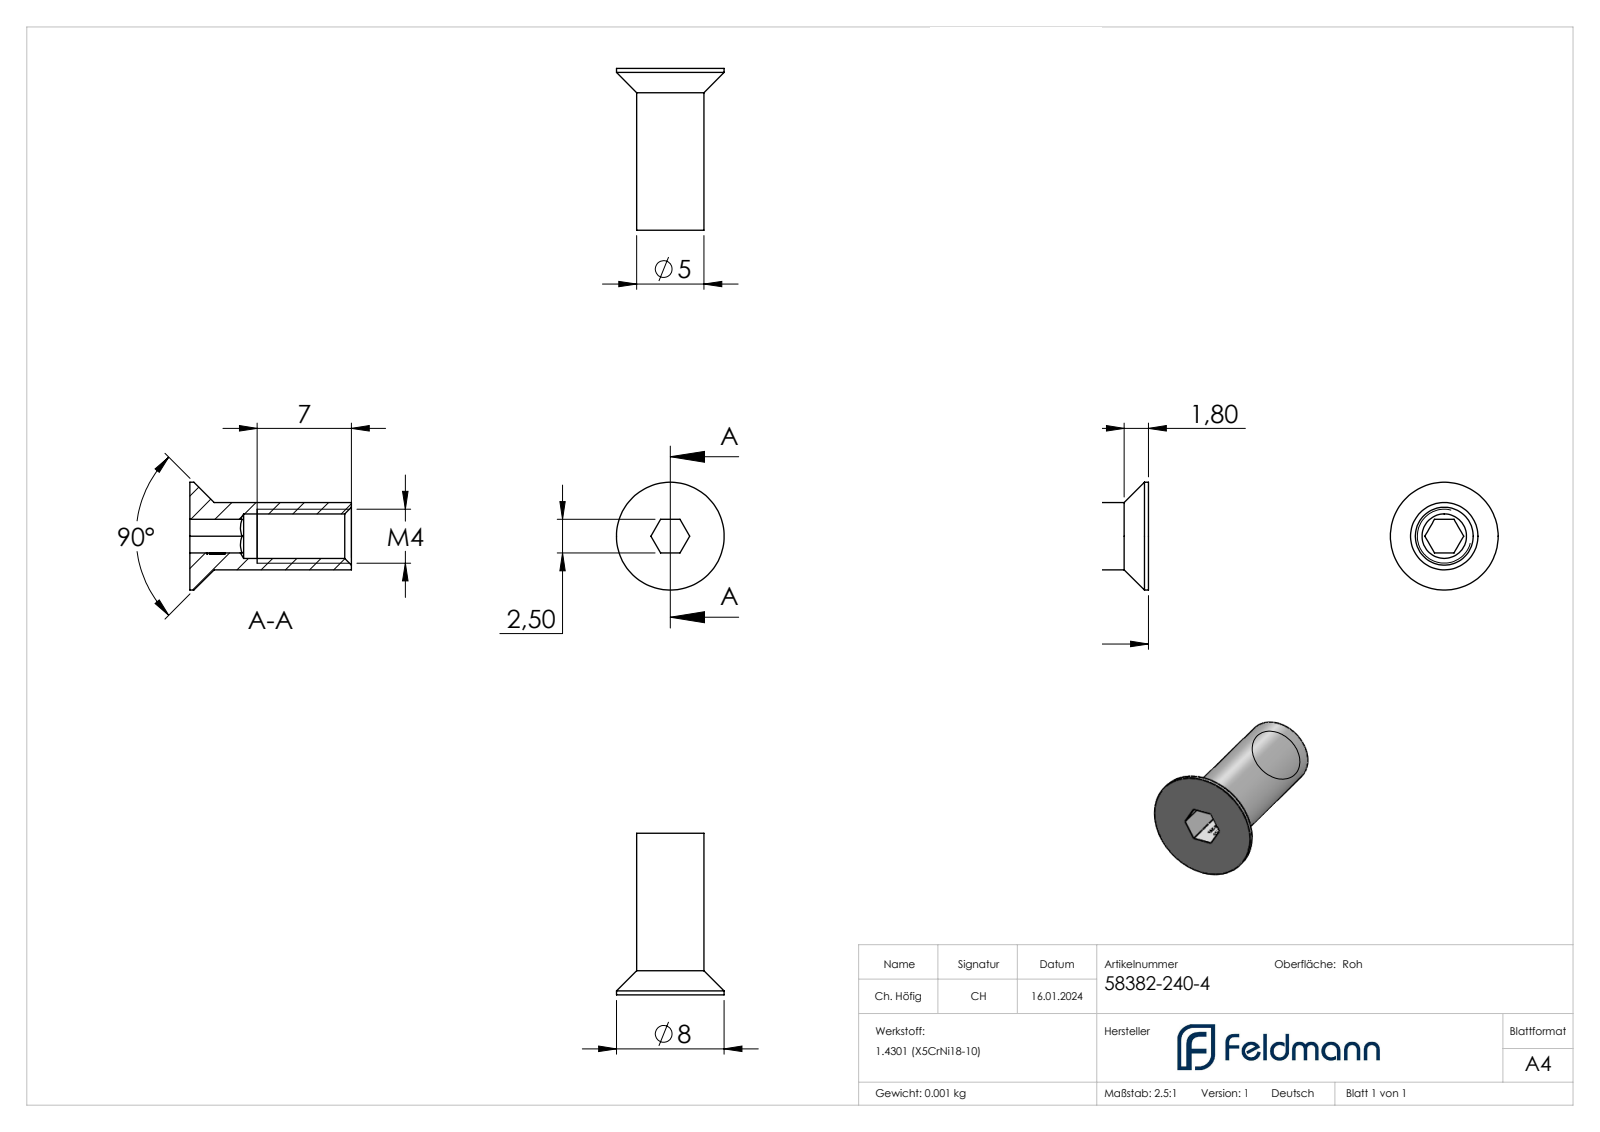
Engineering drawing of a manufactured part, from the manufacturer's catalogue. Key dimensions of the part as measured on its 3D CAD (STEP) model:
Part name (STEP PRODUCT): 58382-240-4
STEP written by: SolidWorks 2018 (CONFIG_CONTROL_DESIGN)
Units: millimetres
Bodies: 1 solid, 287 faces (138 planar, 3 cylindrical, 146 other)
Overall size (bounding box): 25 × 25 × 20.5
Volume: 2 937 mm³ · Surface area: 2 347 mm²
Round holes (diameter × count): ⌀8.5 ×1
Round bosses / shafts (diameter × count): ⌀25 ×1, ⌀14 ×1
Main face-to-face distances: 2.5, 6, 18, 20.5, 6.1, 0.5, 0.52, 0.6, 0.61, 0.63
